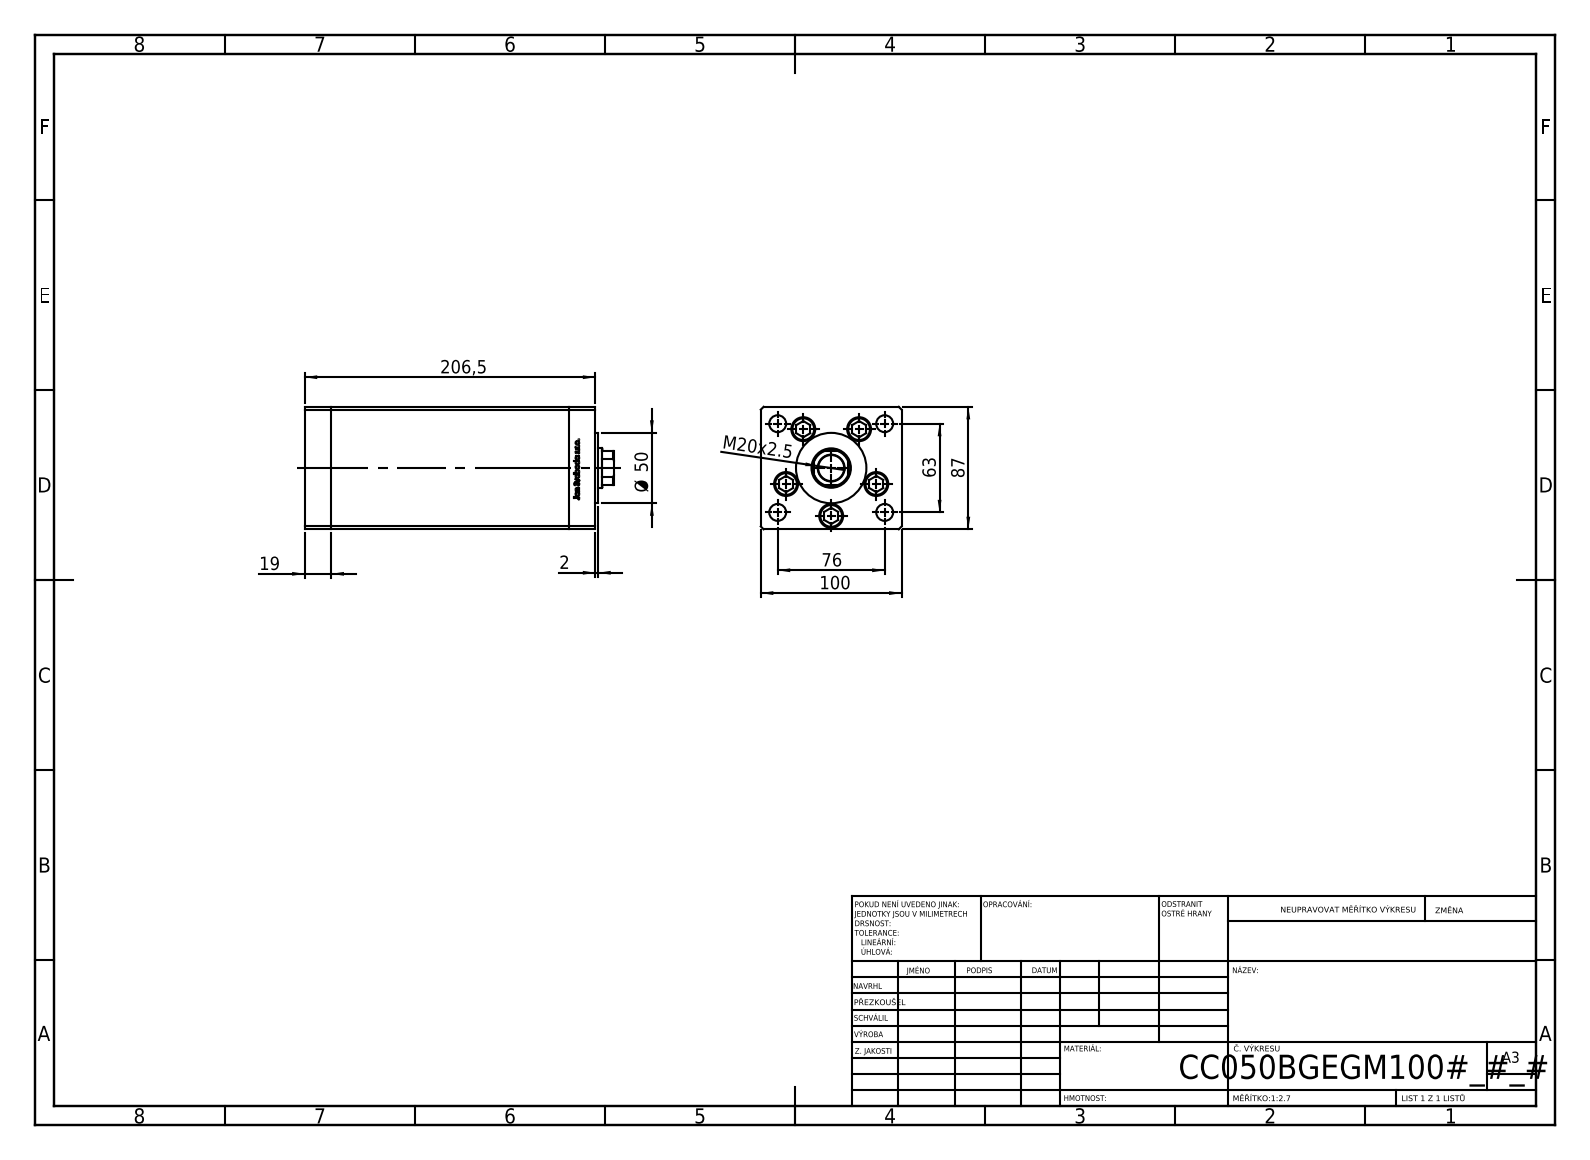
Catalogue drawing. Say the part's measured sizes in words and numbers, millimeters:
The part is named "V220C_B MIDDLE; V220C BACK_B; V220C_FRONT_B; V220C_VC_B (+1 more)". Its 3-D file was written by "SolidWorks 2019 (CONFIG_CONTROL_DESIGN)". It is 14 solids with 1185 faces: 464 planar, 147 cylindrical and 574 other. Overall it measures 219.5 by 100 by 87 millimeters. Its volume is 1 575 000 cubic millimeters and its surface area 218 114 square millimeters. Round holes: 7 of diameter 13.5, 5 of diameter 17, 4 of diameter 12, 2 of diameter 2, 2 of diameter 13.16, 1 of diameter 18.5, 1 of diameter 28. Round bosses or shafts: 5 of diameter 8, 2 of diameter 17, 1 of diameter 50. Partial cylindrical surfaces (rounded edges, fillets, slot ends): 2 of radius 0.93, 1 of radius 13.5. The main face-to-face distances are 100, 87, 19, 168.5, 187.5, 34.25, 206.5, 15.25, 153.25, 172.25. The hole center spacings are 34, 18.59, 39.64, 49.36, 57.95, 21.03, 38.08, 39.27.
